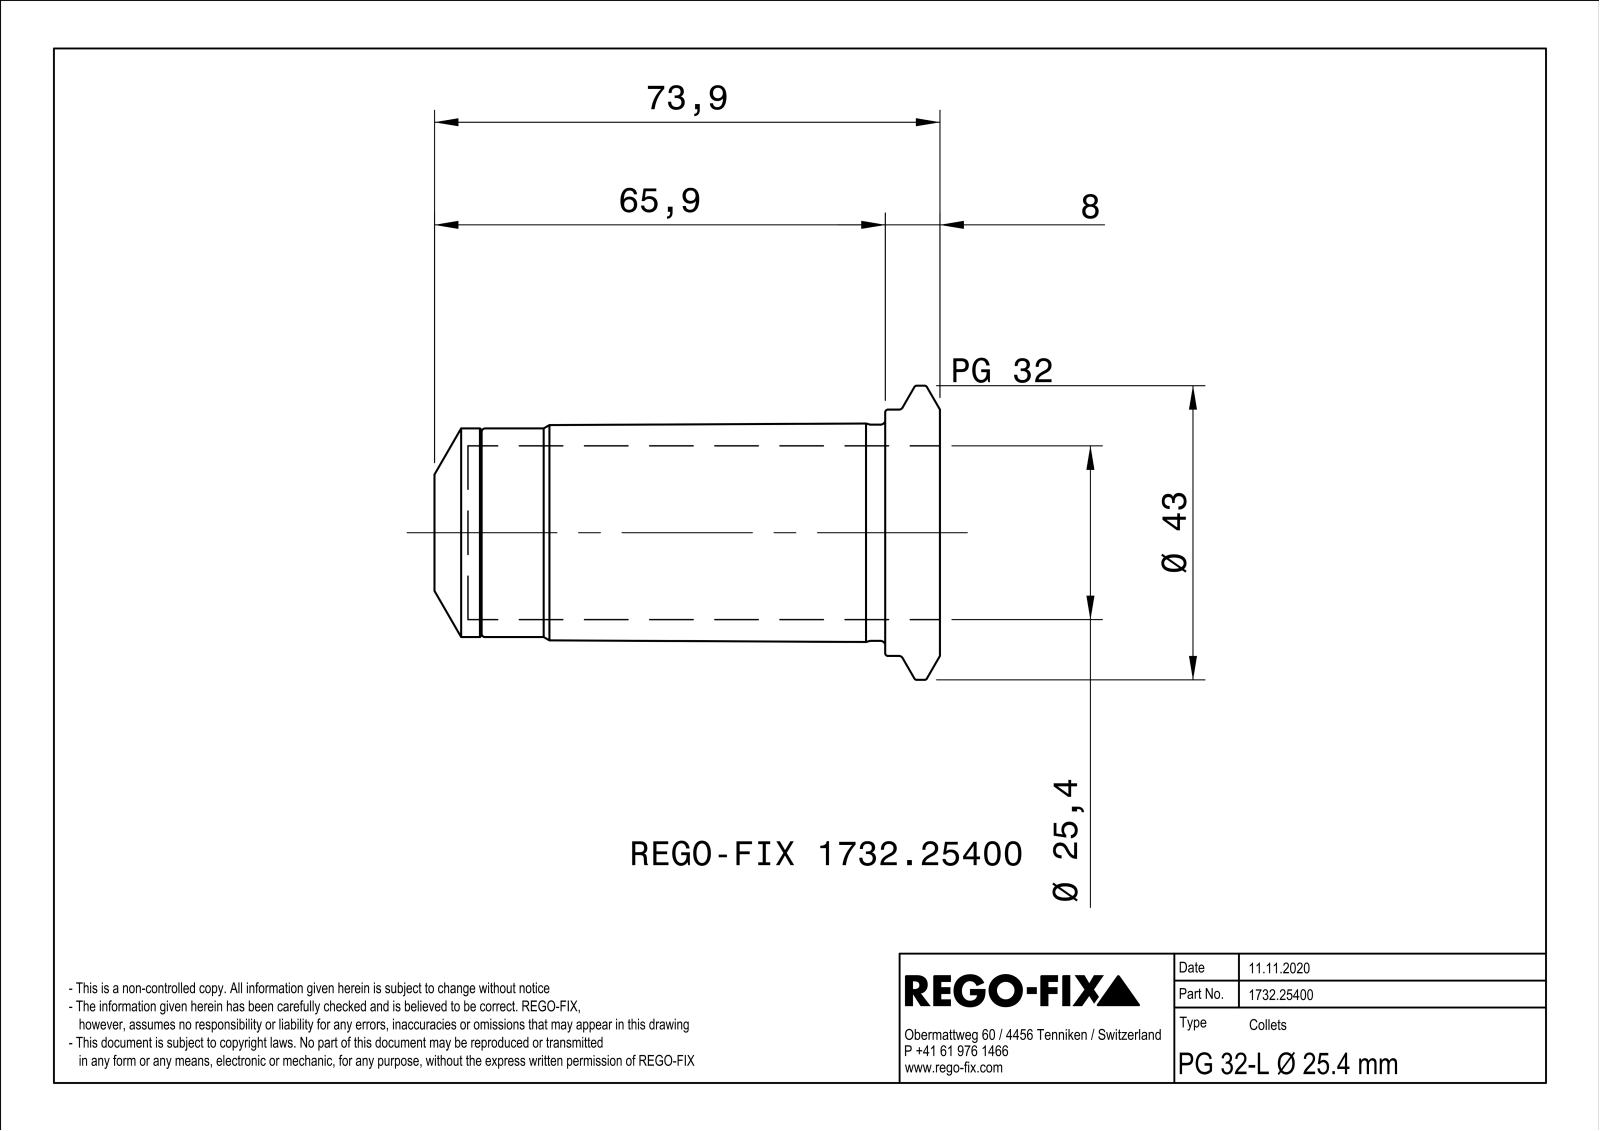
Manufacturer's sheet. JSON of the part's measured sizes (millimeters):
{"part_name": "NOCUT", "step_written_by": "SIEMENS PLM Software Solid Edge ST10 (AUTOMOTIVE_DESIGN)", "units": "millimeters", "bodies": {"solids": 1, "faces": 94, "planar": 29, "cylindrical": 21, "other": 44}, "overall_size": [73.9, 43, 42.99], "volume_mm3": 22386, "surface_area_mm2": 16640, "round_holes": [[5, 1], [25.4, 1], [25.5, 1], [26.92, 1], [28.5, 1]], "round_bosses_or_shafts": [[43, 1], [36, 1], [31.6, 1], [30.5, 1], [26.7, 1]], "partial_cylinders_radius": [[2.5, 3]], "face_to_face_distances": [1, 73.9, 8, 59, 65.9, 58, 50, 15.9, 51, 14.9]}
